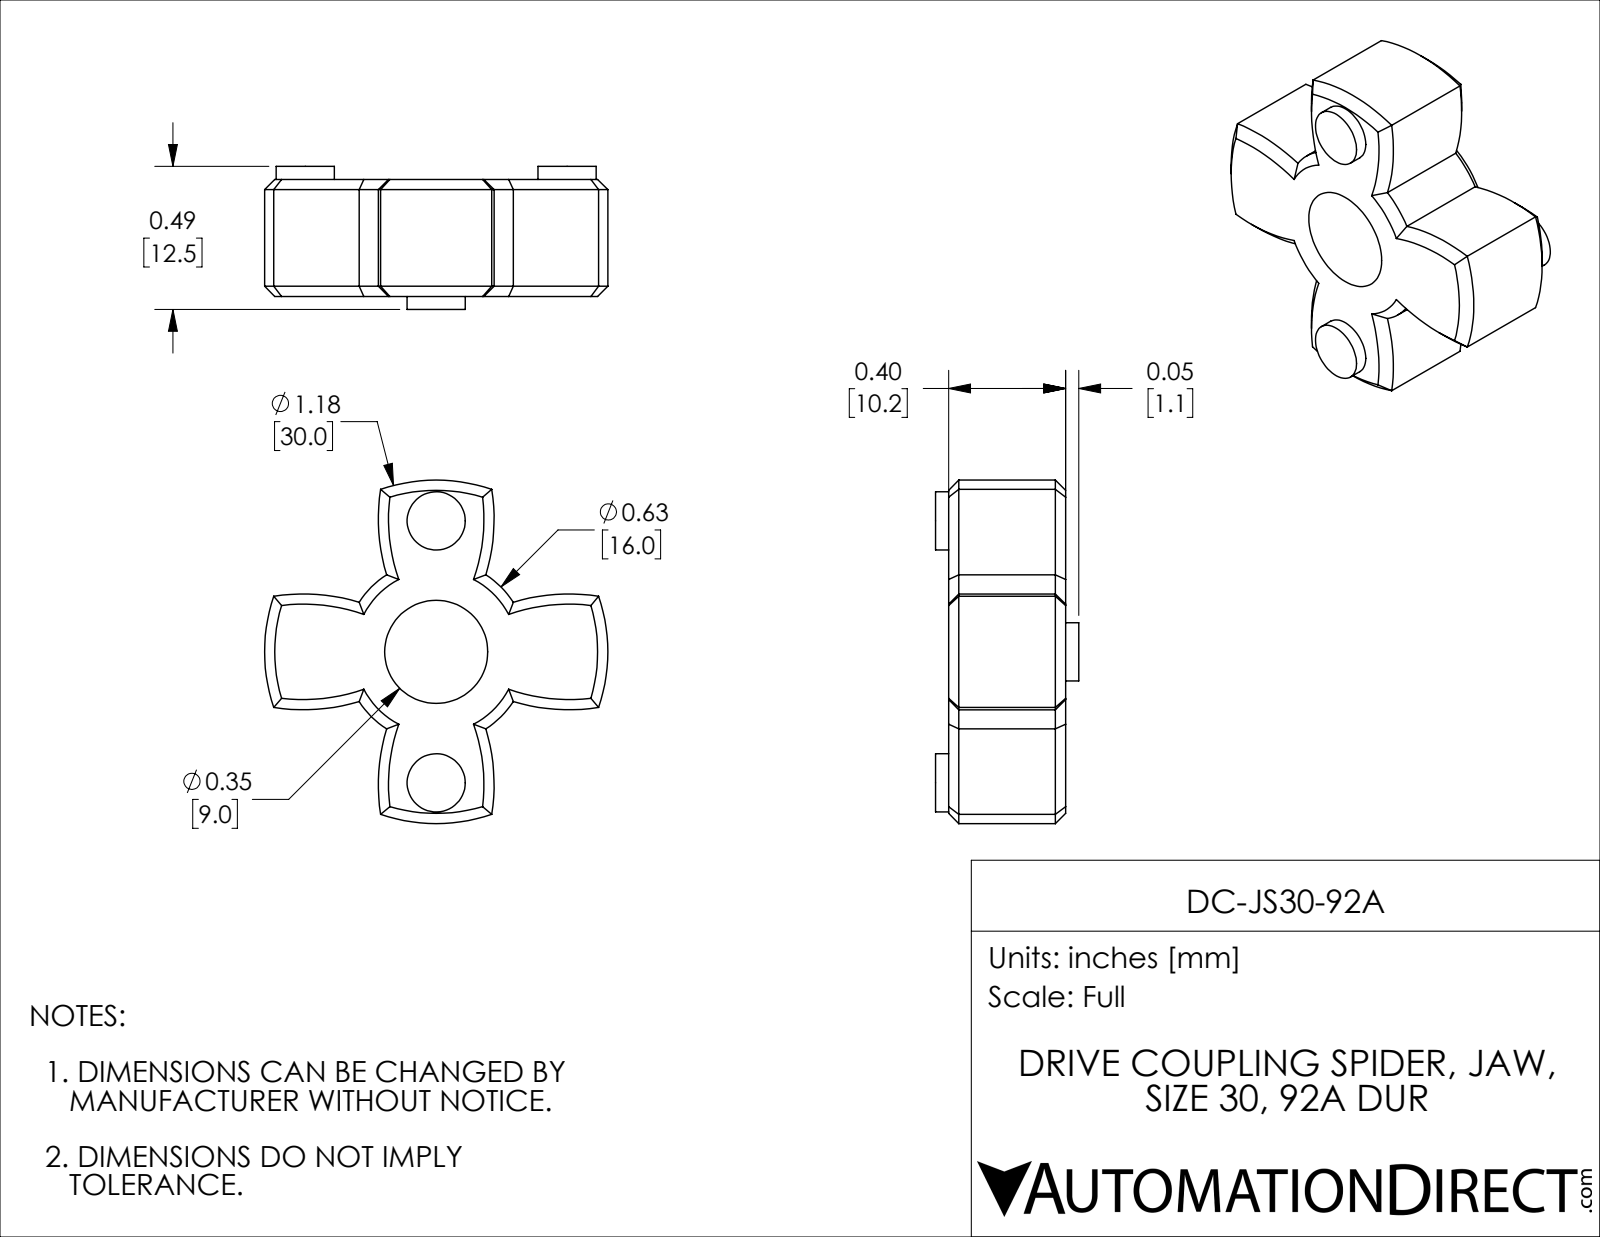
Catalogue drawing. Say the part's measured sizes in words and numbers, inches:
The part is named "DC-JS30-92A". Its 3-D file was written by "SolidWorks 2019 (AUTOMOTIVE_DESIGN)". It is 1 solid with 73 faces: 6 planar, 29 cylindrical and 38 other. Overall it measures 1.18 by 1.18 by 0.492 inches. Its volume is 0.261 cubic inches and its surface area 3.47 square inches. Round holes: 1 of diameter 0.354. Round bosses or shafts: 4 of diameter 0.2. Partial cylindrical surfaces (rounded edges, fillets, slot ends): 4 of radius 0.655, 1 of radius 0.315, 1 of radius 0.59. The main face-to-face distances are 0.402, 0.045, 0.447, 0.492.
